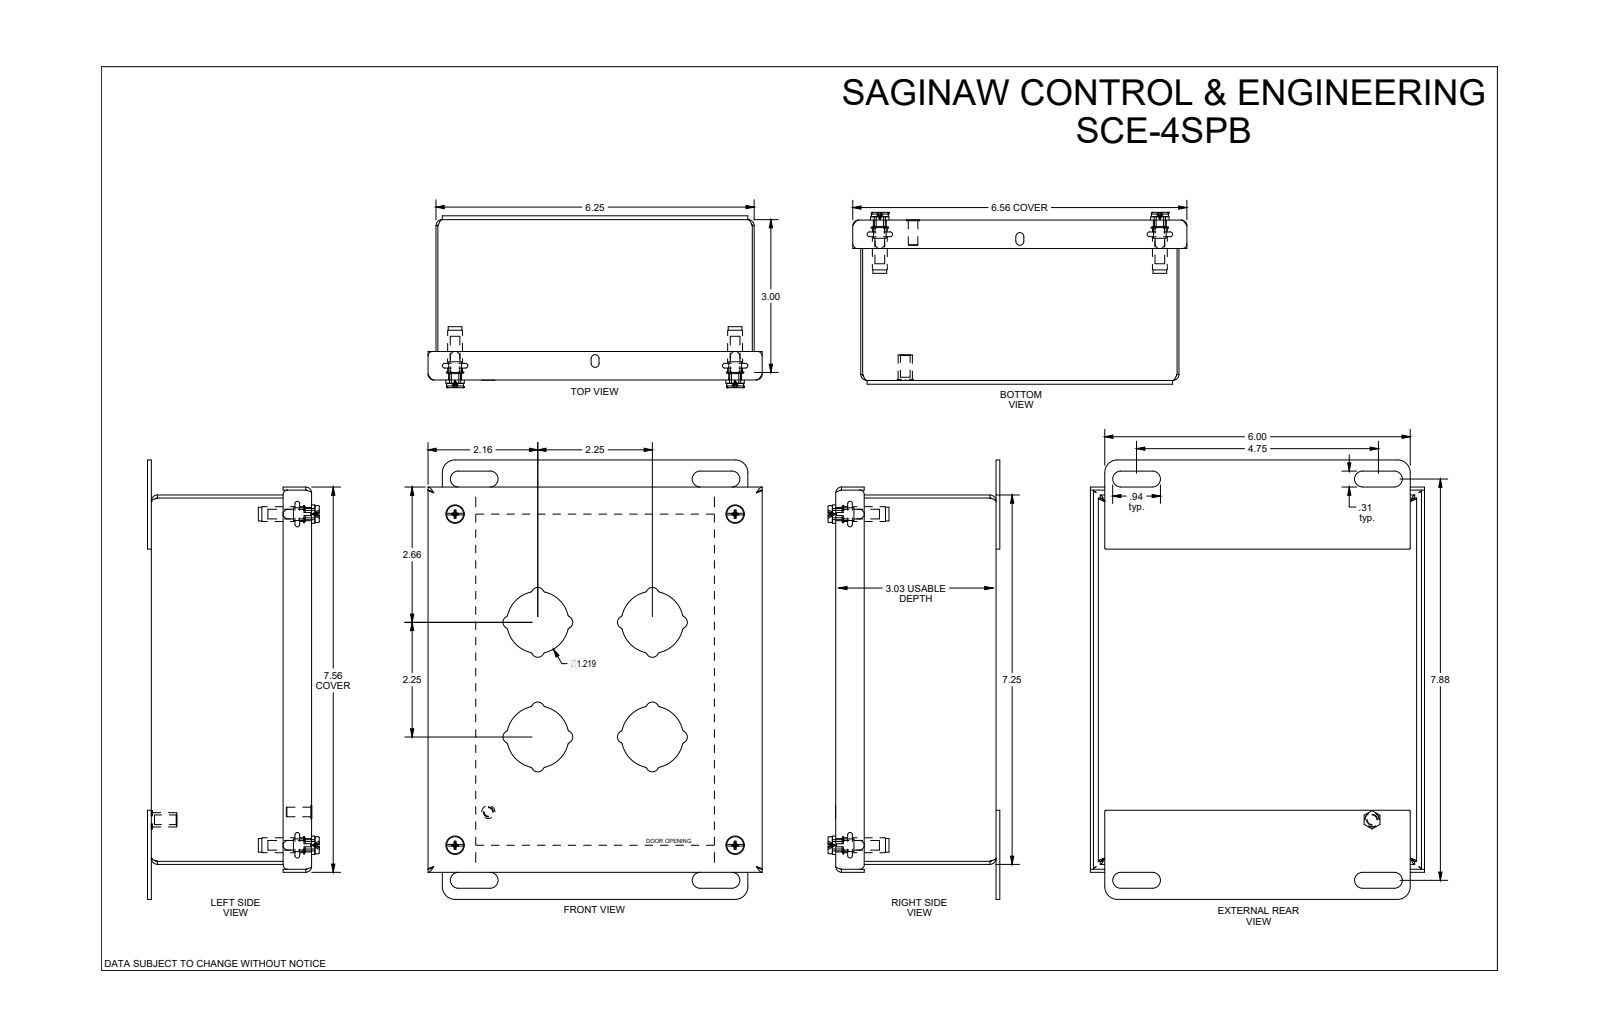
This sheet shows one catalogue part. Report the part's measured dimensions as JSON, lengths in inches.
{"part_name": "SCE-4SPBSS6", "step_written_by": "SolidWorks 2019 (CONFIG_CONTROL_DESIGN)", "units": "inches", "bodies": {"solids": 0, "faces": 790, "planar": 374, "cylindrical": 254, "other": 162}, "overall_size": [8.625, 6.563, 3.374], "round_holes": [[0.19, 5], [0.22, 4], [0.25, 4]], "round_bosses_or_shafts": [[0.188, 5], [0.362, 4], [0.34, 4], [0.334, 4], [0.317, 4], [0.292, 4], [0.27, 4], [0.266, 4]], "partial_cylinders_radius": [[0.04, 32], [0.125, 16], [0.015, 8], [0.052, 8], [0.06, 8], [0.112, 8], [0.115, 8], [0.156, 8]], "face_to_face_distances": [0.06, 3.088, 3.028, 3.148, 6.19, 7.19, 2.94, 0.148, 0.075, 0.135], "hole_center_spacings": [5.5, 6.5, 8.515, 0.707, 5.025, 6.021, 7.81]}
